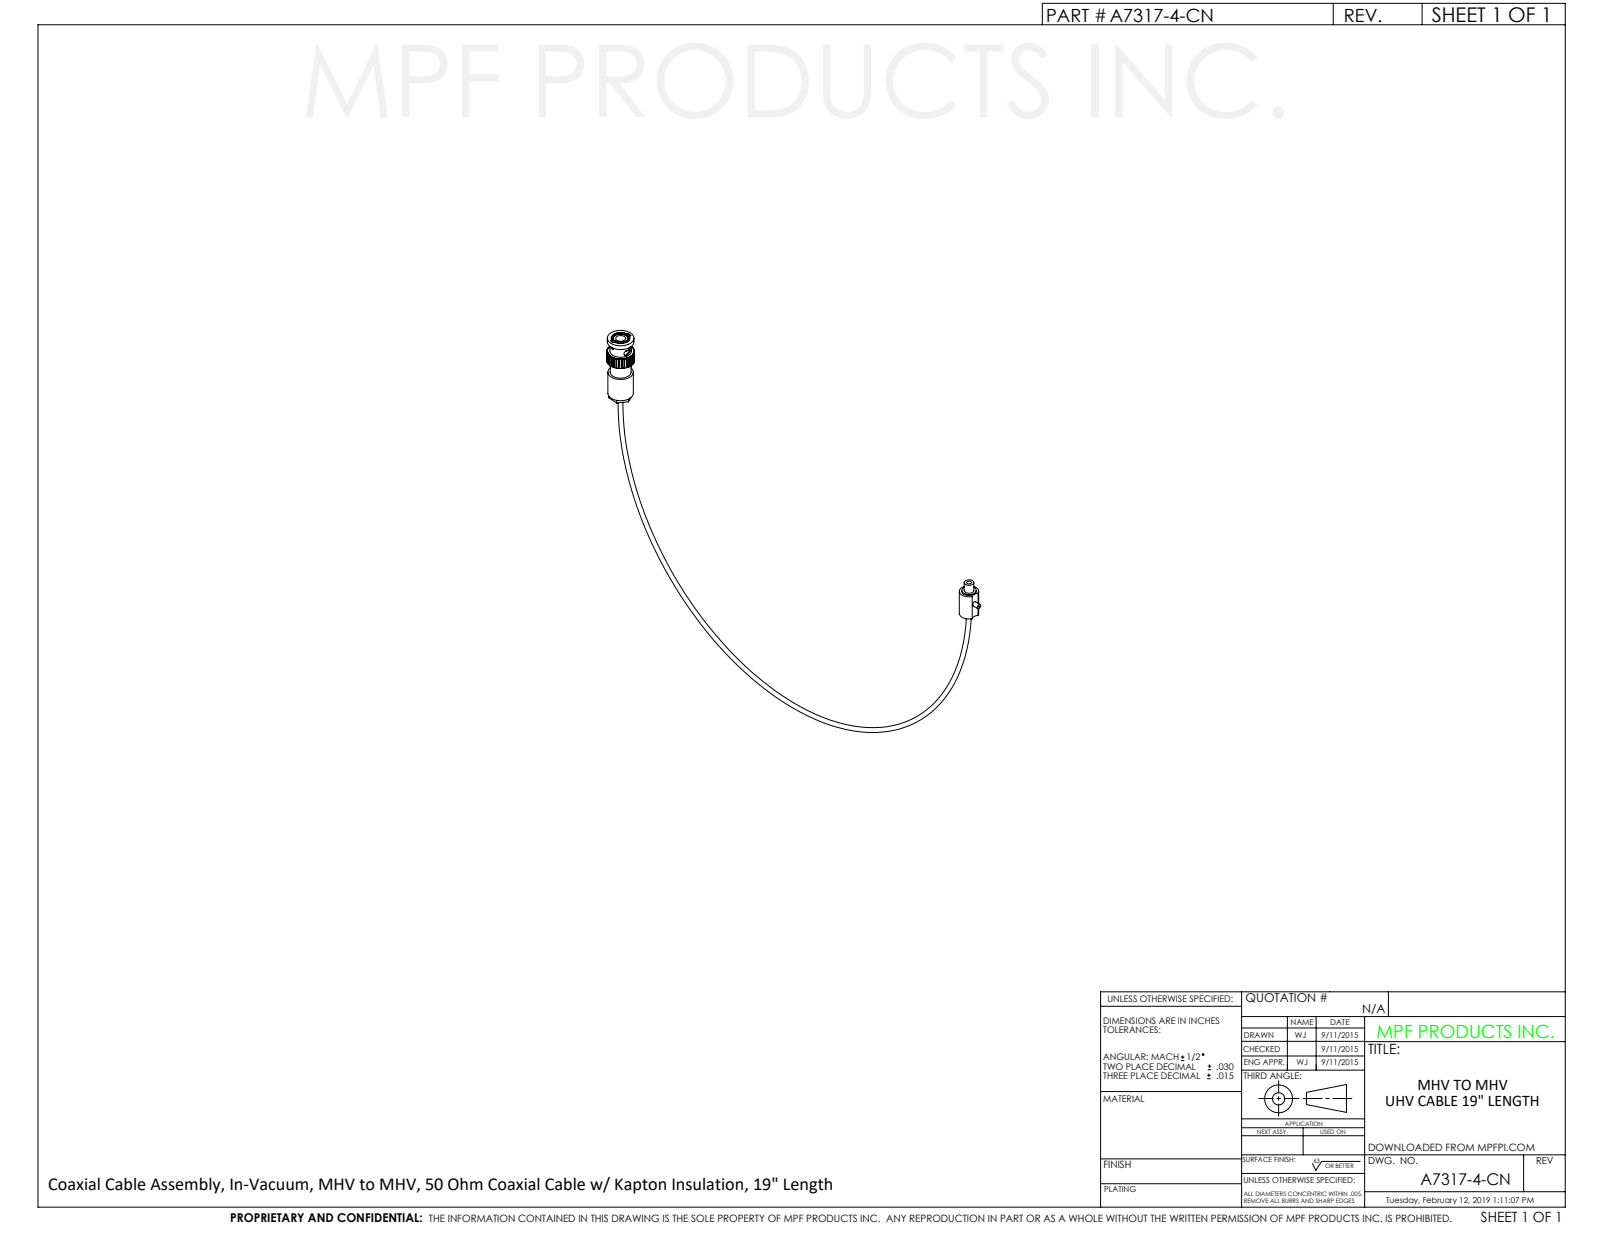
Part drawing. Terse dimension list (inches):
name: A7317-4-CN
written by: SolidWorks 2012 (CONFIG_CONTROL_DESIGN)
unit: in
bodies: 0 solids, 519 faces (360 planar, 157 cylindrical, 2 other)
size: 6.565 × 4.028 × 0.575
holes: 2× ⌀0.158, 2× ⌀0.194, 2× ⌀0.39
bosses: 2× ⌀0.55, 2× ⌀0.525, 2× ⌀0.43, 2× ⌀0.308, 1× ⌀0.445, 1× ⌀0.445, 1× ⌀0.101
rounds: 2× R0.15, 2× R0.151, 2× R0.287, 1× R0.068
face distances: 0.978, 0.014, 0.653, 0.325, 0.878, 0.225, 0.1, 0.385, 0.268, 0.493
hole spacings: 5.99
